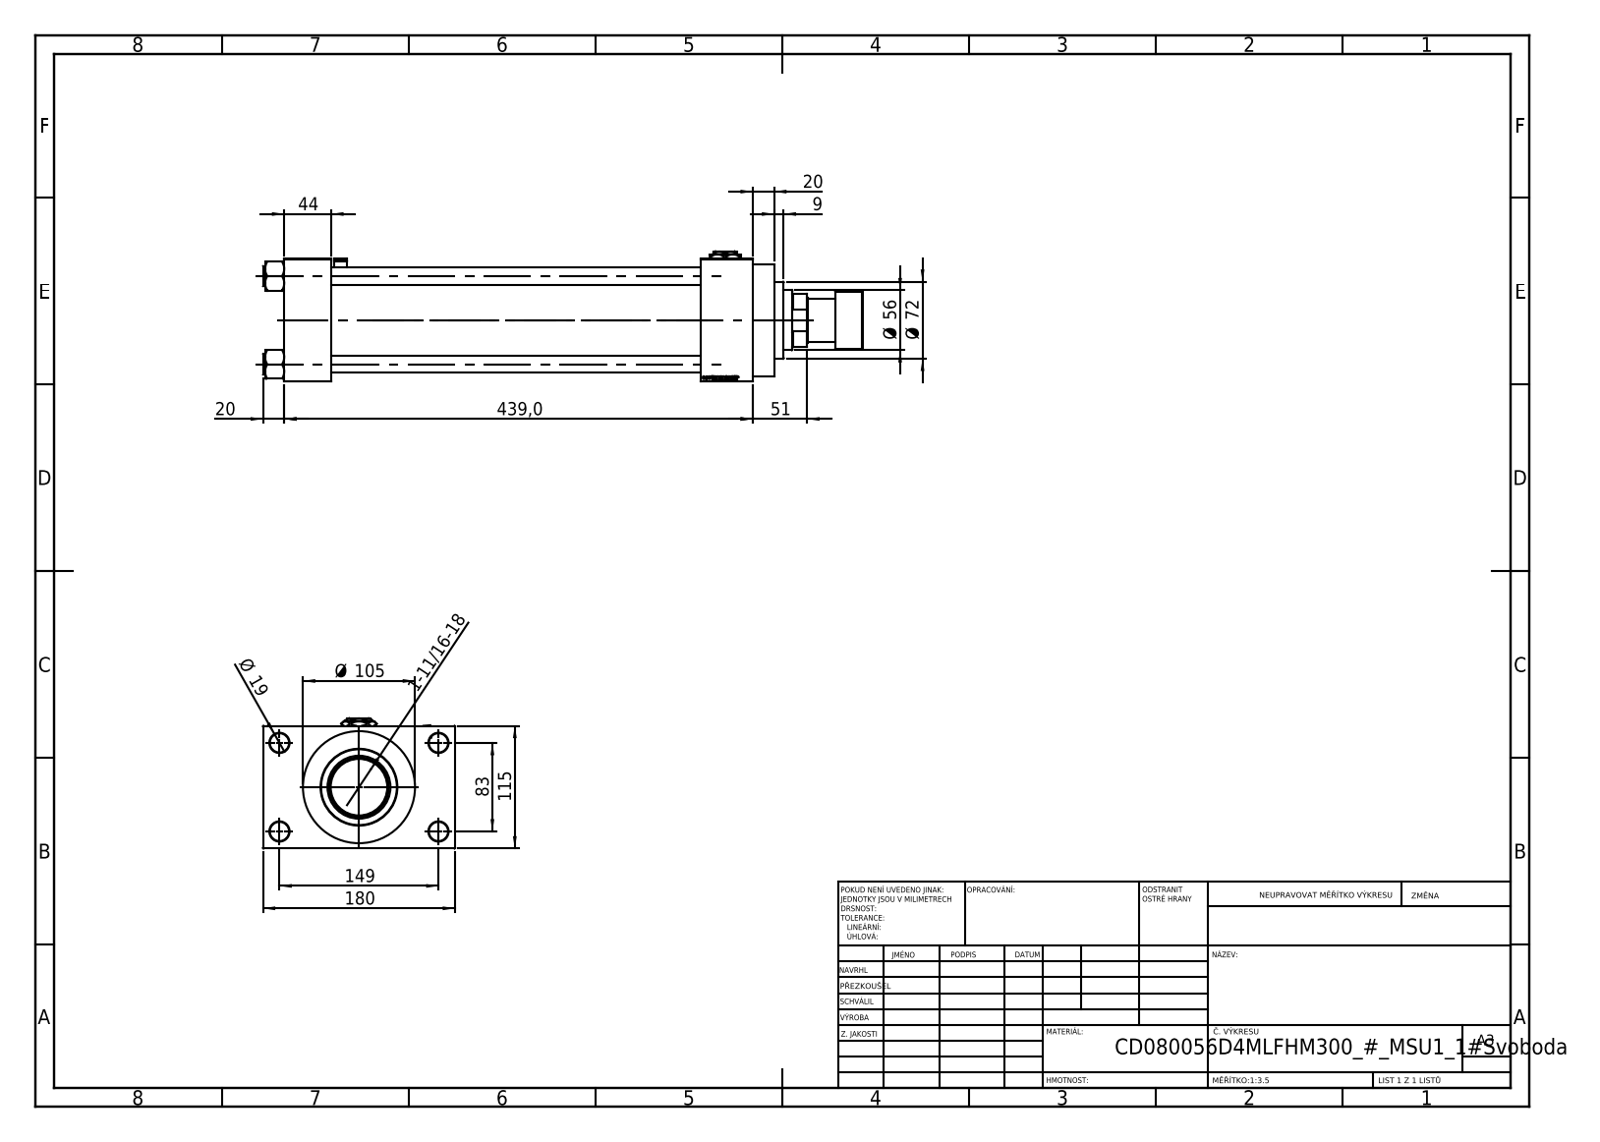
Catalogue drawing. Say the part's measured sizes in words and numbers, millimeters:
The part is named "Zatka_pro_OIL_PORT; V215CR_MSU; V215CD_VC_A; V215CD_NUT_M5_D (+4 more)". Its 3-D file was written by "SolidWorks 2019 (CONFIG_CONTROL_DESIGN)". It is 14 solids with 1282 faces: 599 planar, 121 cylindrical and 562 other. Overall it measures 562 by 180 by 122 millimeters. Its volume is 3 370 000 cubic millimeters and its surface area 580 400 square millimeters. Round holes: 4 of diameter 16, 4 of diameter 18, 2 of diameter 7, 2 of diameter 26.44, 2 of diameter 35, 1 of diameter 40.5, 1 of diameter 56, 1 of diameter 59, 1 of diameter 61, 1 of diameter 72, 1 of diameter 80. Round bosses or shafts: 4 of diameter 19, 1 of diameter 105, 1 of diameter 86, 1 of diameter 54, 1 of diameter 40, 1 of diameter 6. Partial cylindrical surfaces (rounded edges, fillets, slot ends): 24 of radius 0.5, 1 of radius 1, 1 of radius 2.5, 1 of radius 4. The main face-to-face distances are 115, 346, 44, 390, 32.5, 439, 395, 49, 147.5, 20. The hole center spacings are 33.15, 58.48, 82.7, 85.28, 89.24, 115.85, 142.43, 83.
